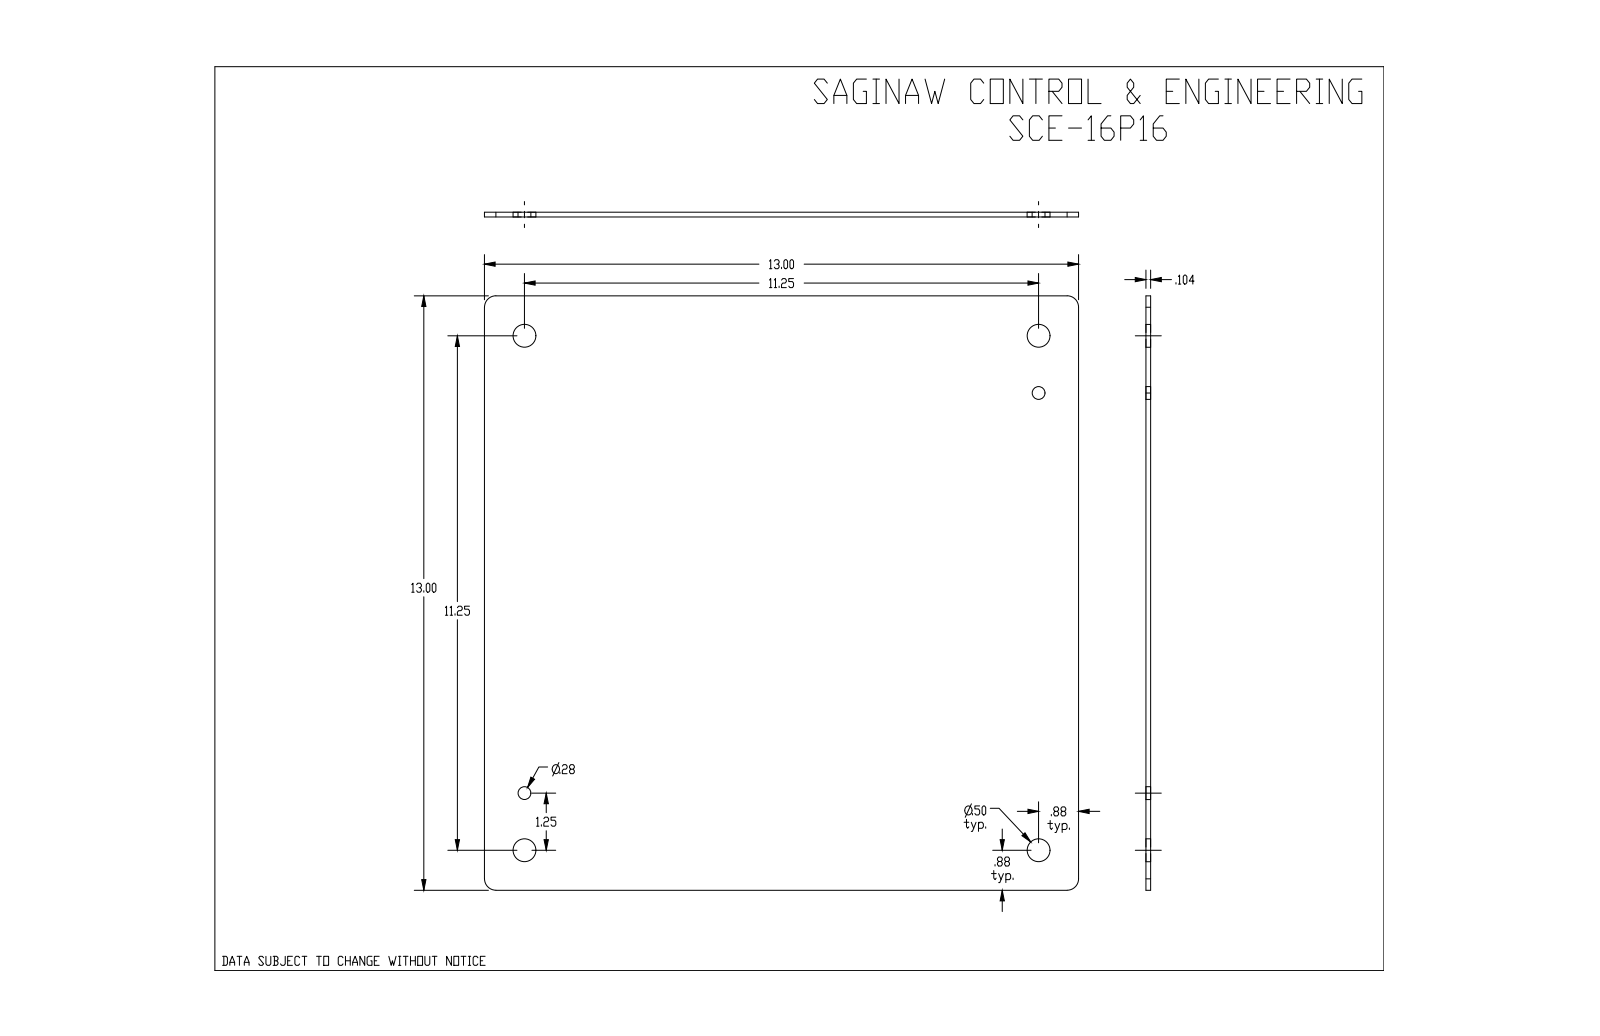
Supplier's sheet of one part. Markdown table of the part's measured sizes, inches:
| quantity | value |
| --- | --- |
| part name | SCE-16P16 |
| STEP written by | SolidWorks 2019 (CONFIG_CONTROL_DESIGN) |
| units | inches |
| bodies | 1 solid, 16 faces (6 planar, 10 cylindrical, 0 other) |
| overall size | 13 × 13 × 0.104 |
| volume | 17.48 in³ |
| surface area | 342.3 in² |
| round holes (diameter × count) | 0.5 × 4, 0.281 × 1, 0.281 × 1 |
| partial cylindrical surfaces (radius × count) | 0.25 × 4 |
| main face-to-face distances | 0.104, 13 |
| hole center spacings | 11.25, 1.25, 10, 11.32, 15.052, 15.911, 14.252 |
